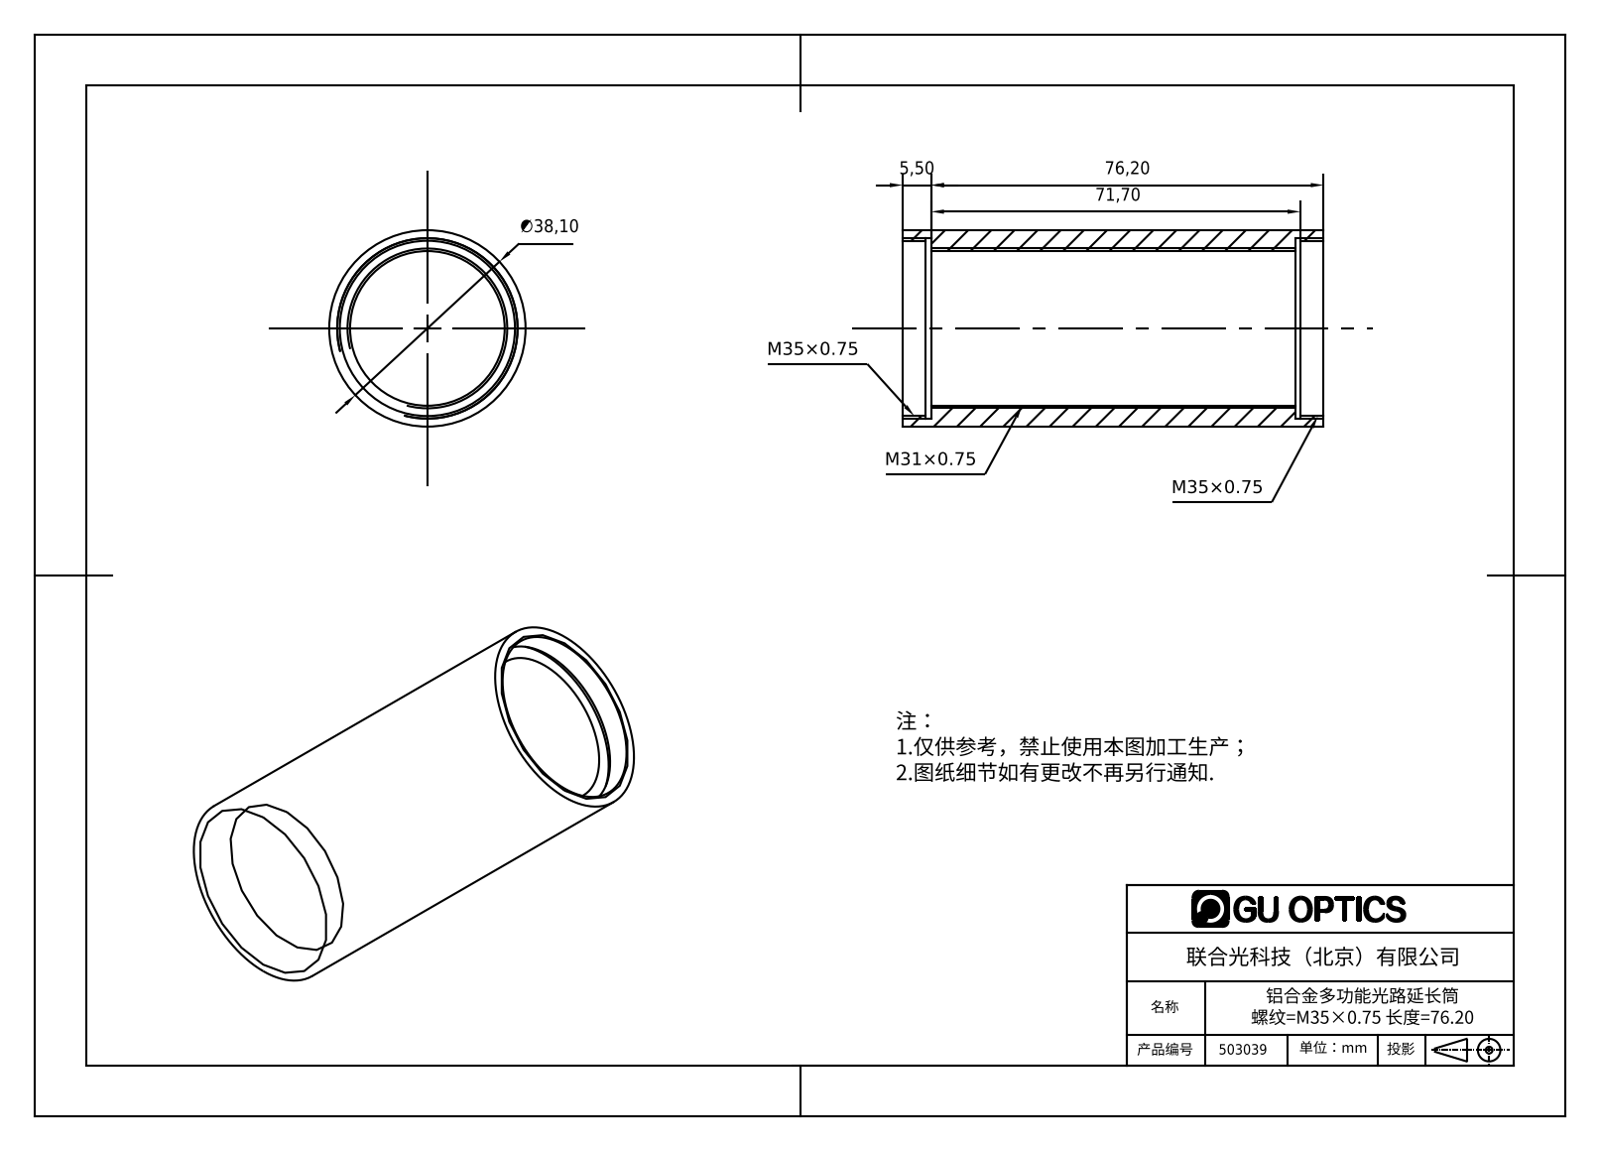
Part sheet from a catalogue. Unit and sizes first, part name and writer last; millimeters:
Units: millimetres
Overall size (bounding box): 81.7 × 38.1 × 38.1
Round holes (diameter × count): ⌀30 ×1, ⌀34 ×1, ⌀35.2 ×1
Round bosses / shafts (diameter × count): ⌀38.1 ×1
Main face-to-face distances: 5.5, 76.2, 70.7, 81.7, 4.5, 77.2, 1, 71.7, 72.7
Volume: 33 053 mm³ · Surface area: 18 752 mm²
Bodies: 1 solid, 18 faces (6 planar, 12 cylindrical, 0 other)
Part name (STEP PRODUCT): 503039
STEP written by: SolidWorks 2016 (AUTOMOTIVE_DESIGN)
